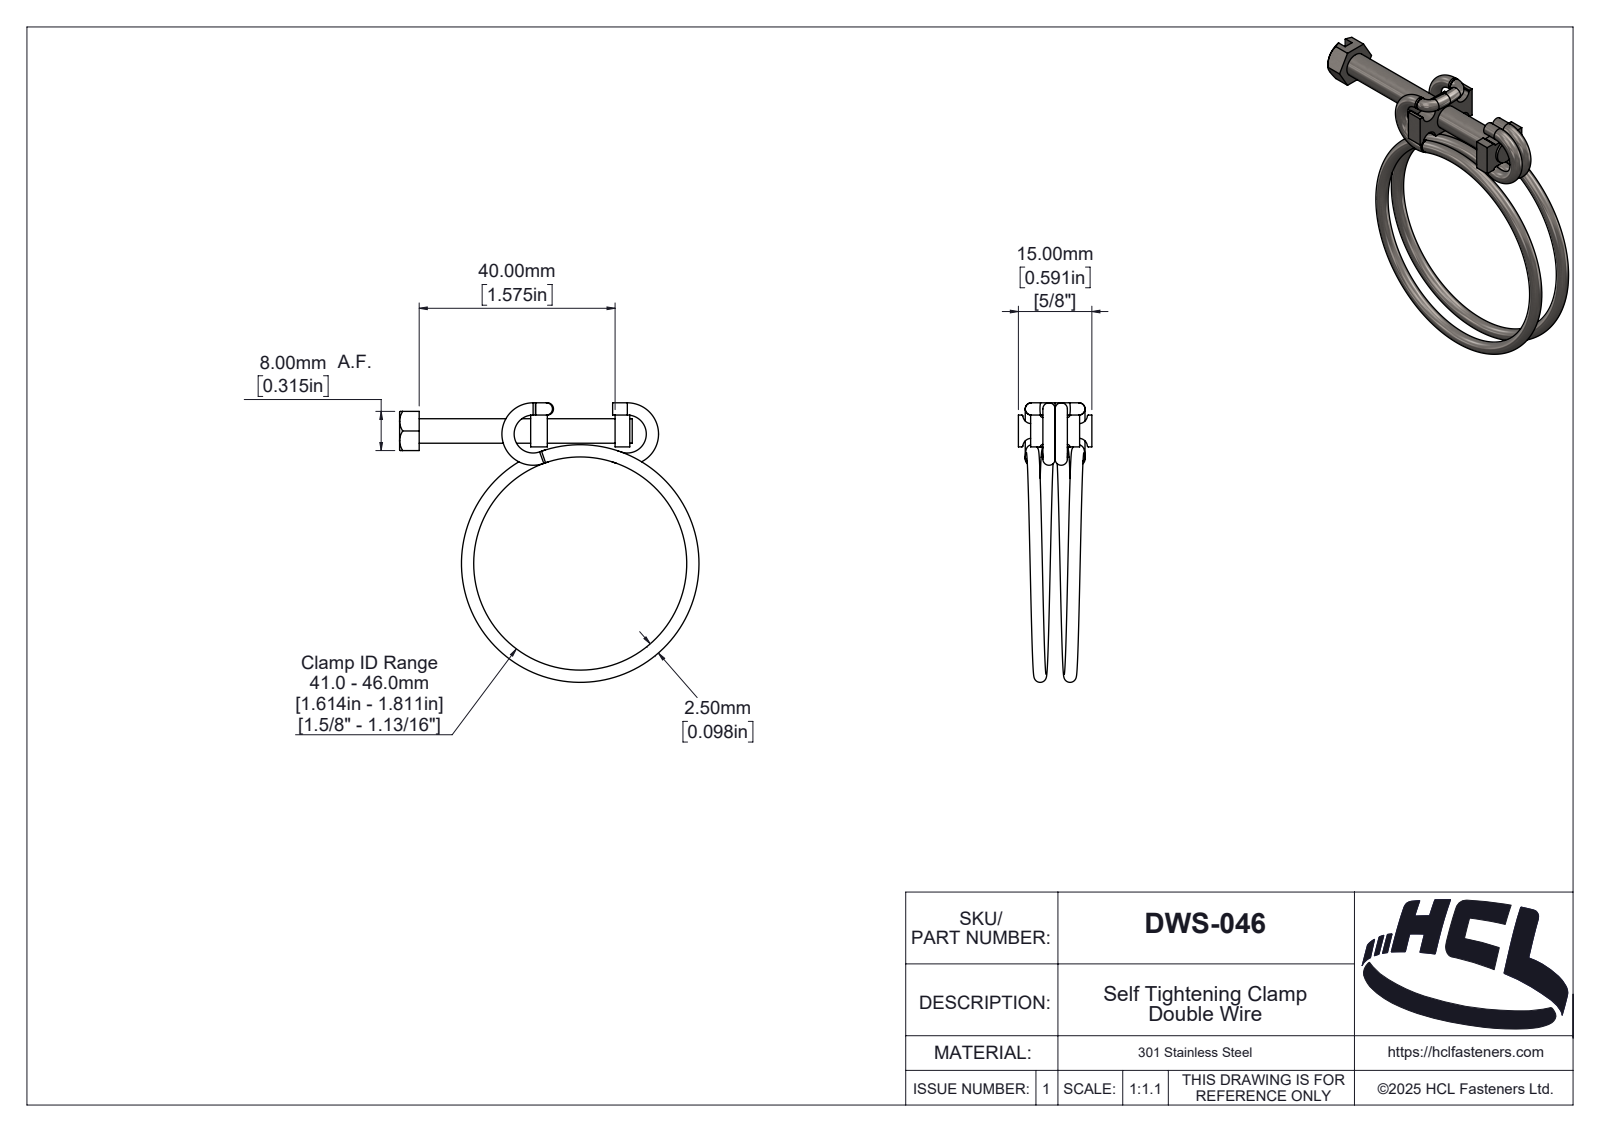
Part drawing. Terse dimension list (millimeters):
name: DWS-046
written by: SolidWorks 2025 (AUTOMOTIVE_DESIGN)
unit: mm
bodies: 6 solids, 213 faces (55 planar, 74 cylindrical, 84 other)
size: 61.13 × 57.05 × 15
volume: 3 382 mm³; area: 4 760 mm²
holes: 1× ⌀5
bosses: 4× ⌀2.5
rounds: 12× R0.2, 4× R0.5, 4× R1.75, 1× R0.4, 1× R0.51, 1× R0.53, 1× R0.64, 1× R0.91
face distances: 4, 6.5, 6, 0.5, 3.4, 2, 20.24, 16.84, 17.24, 13.84
